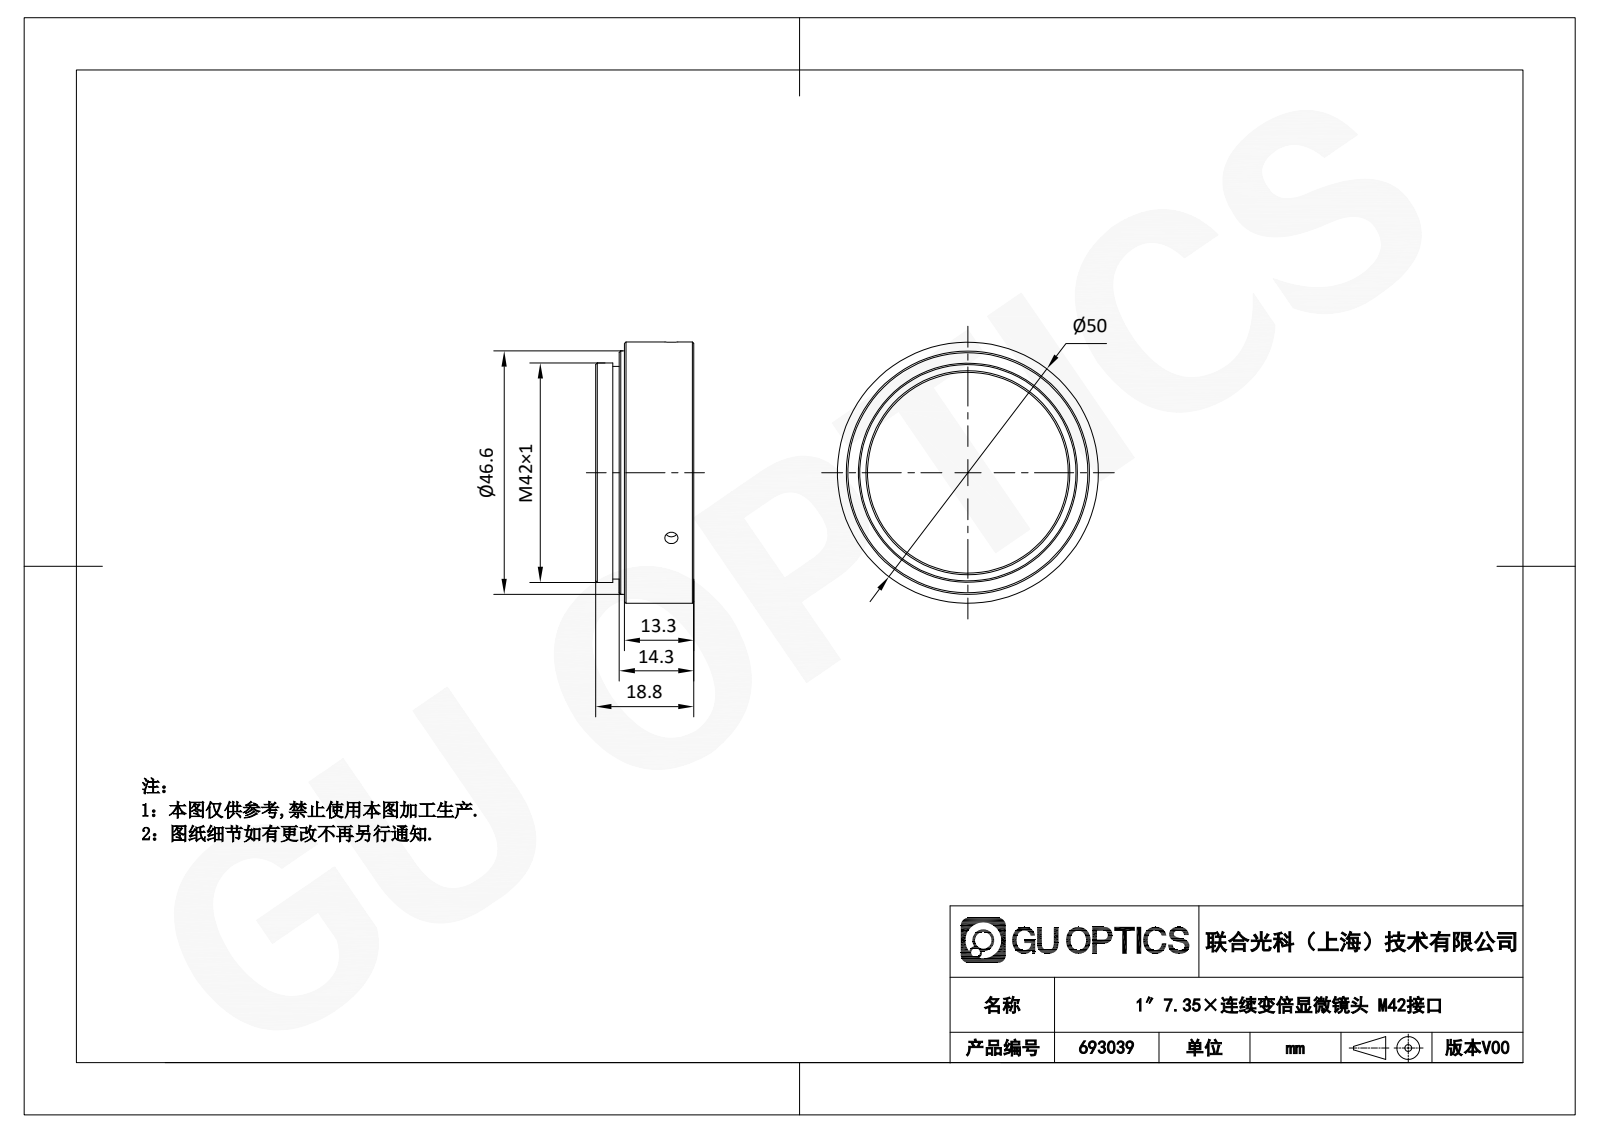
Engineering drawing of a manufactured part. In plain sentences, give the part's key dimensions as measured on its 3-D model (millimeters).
The part is named "693039". Its 3-D file was written by "SolidWorks 2020 (CONFIG_CONTROL_DESIGN)". It is 1 solid with 51 faces: 20 planar, 10 cylindrical and 21 other. Overall it measures 50 by 50 by 18.8 millimeters. Its volume is 6 890 cubic millimeters and its surface area 7 492 square millimeters. Round holes: 3 of diameter 2.5, 1 of diameter 38.5, 1 of diameter 44.8. Round bosses or shafts: 1 of diameter 50, 1 of diameter 46.6, 1 of diameter 42, 1 of diameter 40.7. The main face-to-face distances are 2.1, 1.2, 0.4, 0.8, 12.2, 14.3, 1.6, 2, 3.3, 2.4.
